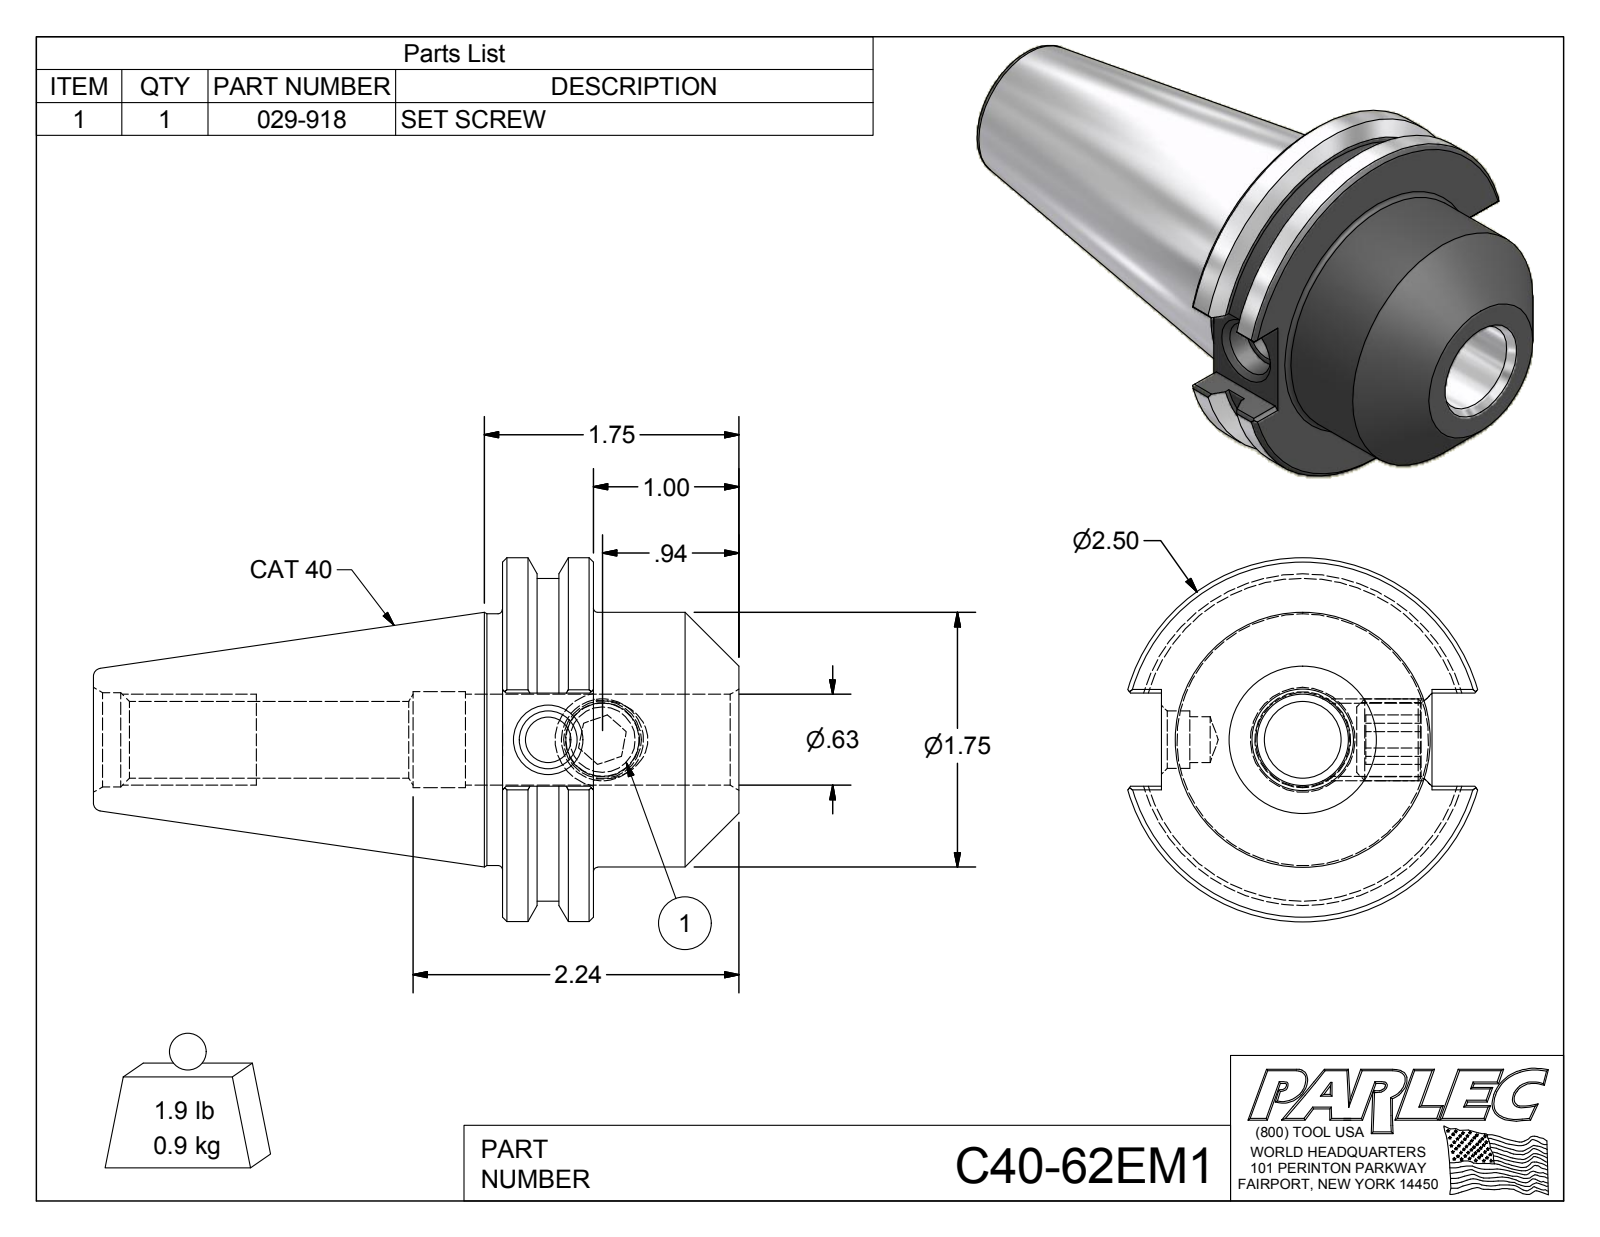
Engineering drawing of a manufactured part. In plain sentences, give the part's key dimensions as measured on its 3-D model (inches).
The part is named "C40-62EM1; C40-62EM1-1; 029-918". Its 3-D file was written by "Autodesk Inventor 2012 (AUTOMOTIVE_DESIGN)". It is 2 solids with 81 faces: 42 planar, 16 cylindrical and 23 other. Overall it measures 4.438 by 2.5 by 2.403 inches. Its volume is 7.731 cubic inches and its surface area 39.82 square inches. Round holes: 1 of diameter 0.315, 1 of diameter 0.396, 1 of diameter 0.502, 1 of diameter 0.527, 1 of diameter 0.625, 1 of diameter 0.648, 1 of diameter 0.66. Round bosses or shafts: 1 of diameter 2.5, 1 of diameter 2.219, 1 of diameter 1.75, 1 of diameter 1.73, 1 of diameter 0.563. The main face-to-face distances are 0.625, 1.625, 1, 0.64, 1.86, 0.3, 2.813, 3.437, 4.437, 3.201. The hole center spacings are 0.372.
